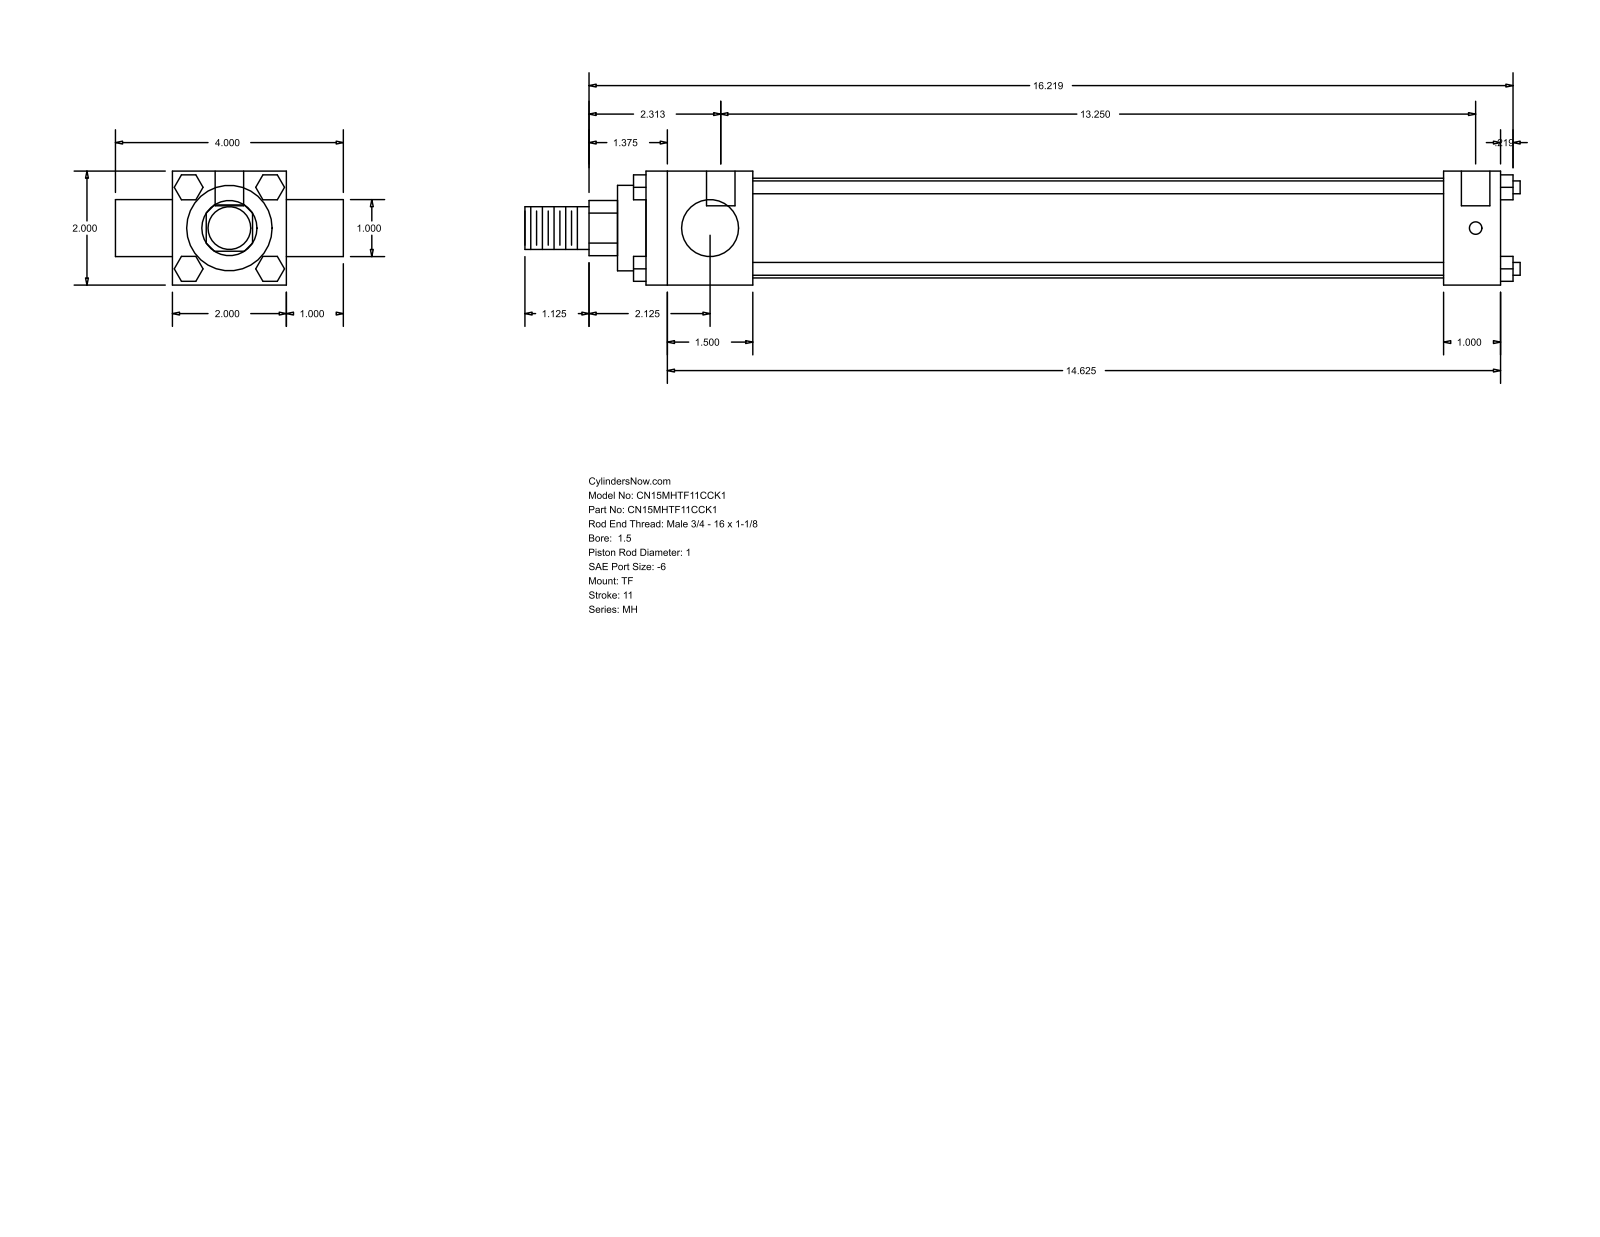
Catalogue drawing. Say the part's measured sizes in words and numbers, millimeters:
The part is named "MH_TF__0150_1". Its 3-D file was written by "GSSL Pune (CONFIG_CONTROL_DESIGN)". It is 0 solids with 120 faces: 92 planar, 28 cylindrical and 0 other. Overall it measures 443.71 by 101.6 by 50.8 millimeters. Round holes: 3 of diameter 5.56, 2 of diameter 12.7. Round bosses or shafts: 4 of diameter 5.71, 2 of diameter 25.4, 1 of diameter 44.45, 1 of diameter 38.1, 1 of diameter 19.05. Partial cylindrical surfaces (rounded edges, fillets, slot ends): 1 of radius 12.29. The main face-to-face distances are 50.8, 25.4, 381, 76.2, 47.63, 333.37, 355.6, 307.97, 101.6, 12.7. The hole center spacings are 3.18, 336.55, 339.73.
